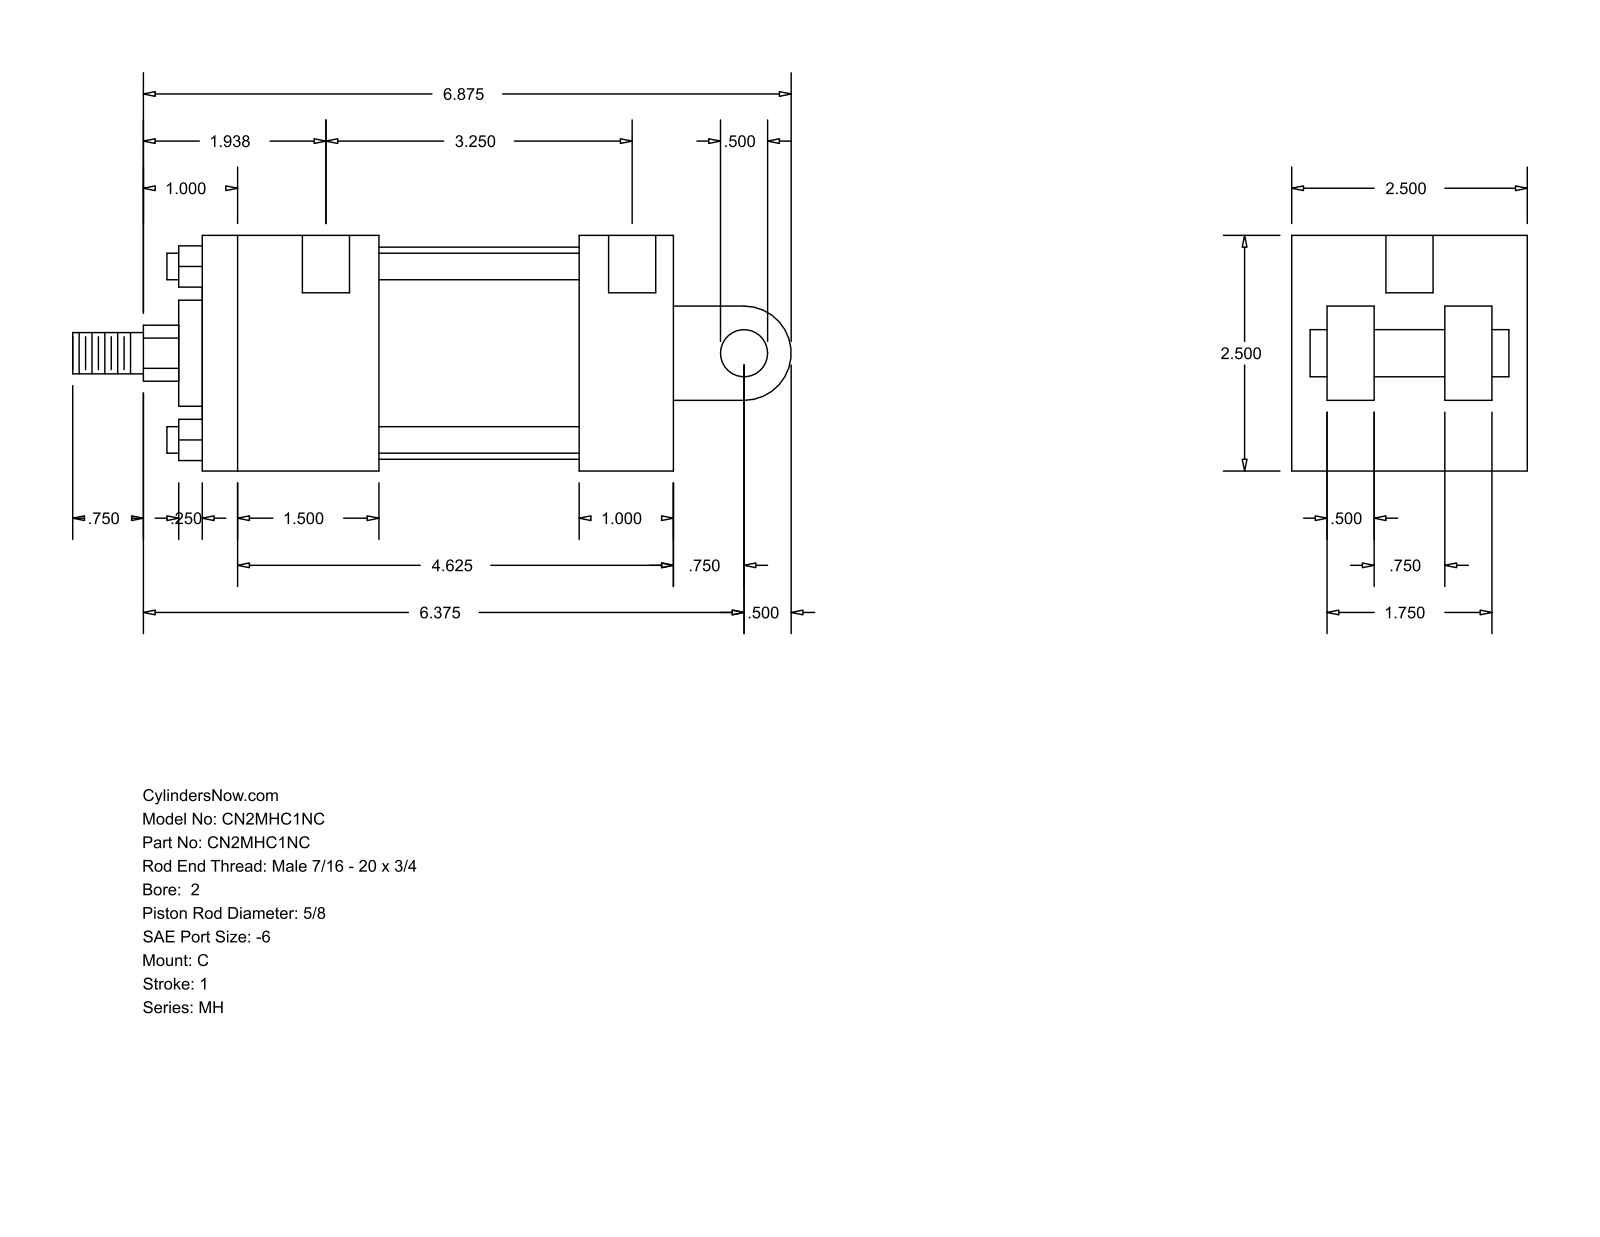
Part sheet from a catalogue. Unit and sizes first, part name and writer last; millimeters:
Units: millimetres
Overall size (bounding box): 193.68 × 63.5 × 63.5
Round holes (diameter × count): ⌀5.56 ×4, ⌀12.7 ×2
Round bosses / shafts (diameter × count): ⌀7.14 ×4, ⌀57.15 ×1, ⌀28.57 ×1, ⌀15.88 ×1, ⌀12.7 ×1, ⌀11.11 ×1
Partial cylindrical surfaces — rounded edges, fillets, slot ends (radius × count): R7.54 ×1, R12.7 ×1
Main face-to-face distances: 63.5, 127, 53.97, 12.7, 47.62, 101.59, 79.38, 25.41, 19.05, 22.22
Hole centre spacings: 90.49, 3.18, 4.76, 82.55, 85.73, 87.31
Bodies: 0 solids, 99 faces (70 planar, 29 cylindrical, 0 other)
Part name (STEP PRODUCT): MH_C__0200_0.625
STEP written by: GSSL Pune (CONFIG_CONTROL_DESIGN)
